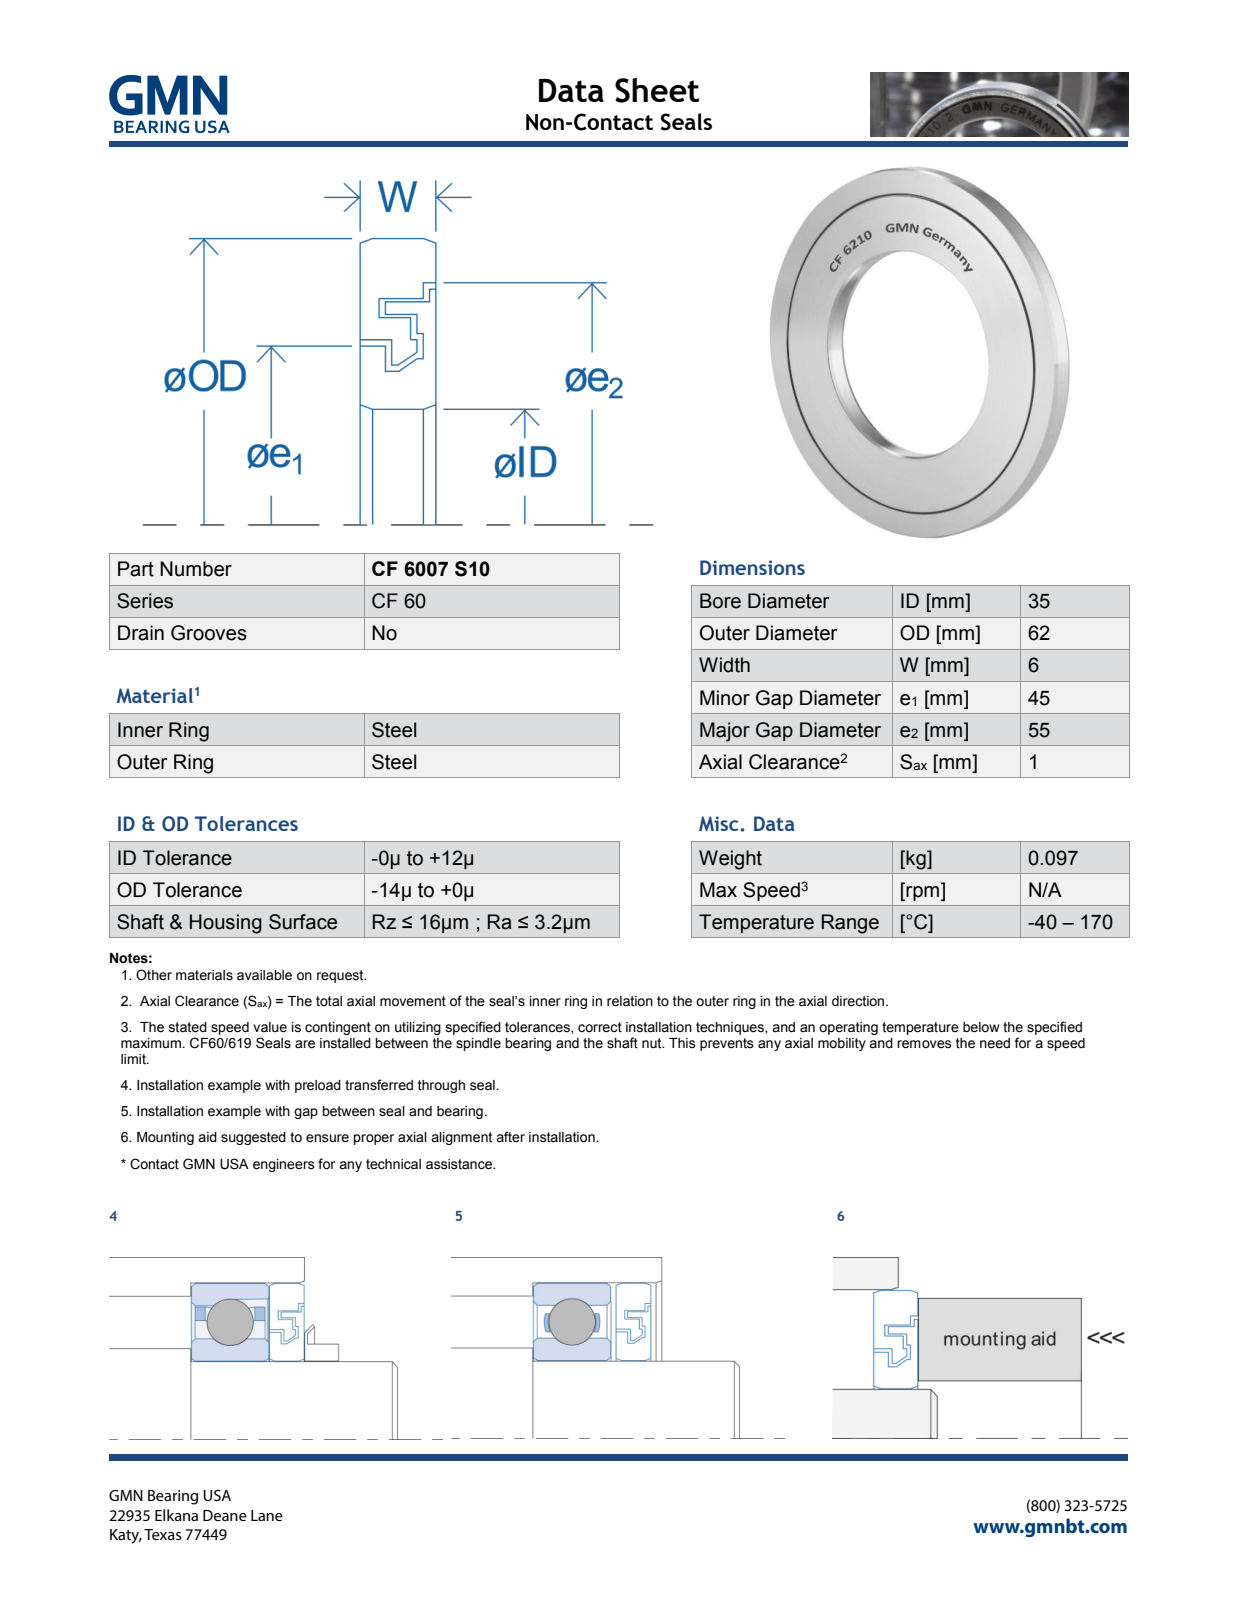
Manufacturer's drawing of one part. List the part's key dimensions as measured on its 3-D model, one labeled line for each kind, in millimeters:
Part name (STEP PRODUCT): CF6007S10_PRT
STEP written by: PRO/ENGINEER BY PARAMETRIC TECHNOLOGY CORPORATION, 2013150 (AUTOMOTIVE_DESIGN)
Units: millimetres
Bodies: 2 solids, 653 faces (611 planar, 30 cylindrical, 12 other)
Overall size (bounding box): 62 × 62 × 6.05
Volume: 11 003 mm³ · Surface area: 11 576 mm²
Round holes (diameter × count): ⌀35 ×1, ⌀42 ×1, ⌀46 ×1, ⌀47 ×1, ⌀50 ×1, ⌀52.5 ×1, ⌀55 ×1
Round bosses / shafts (diameter × count): ⌀62 ×1, ⌀54 ×1, ⌀52 ×1, ⌀49.5 ×1, ⌀45 ×1, ⌀43 ×1, ⌀41 ×1
Main face-to-face distances: 6, 0.5, 2, 1, 2.5, 1.5, 4, 3, 3.5, 4.5
